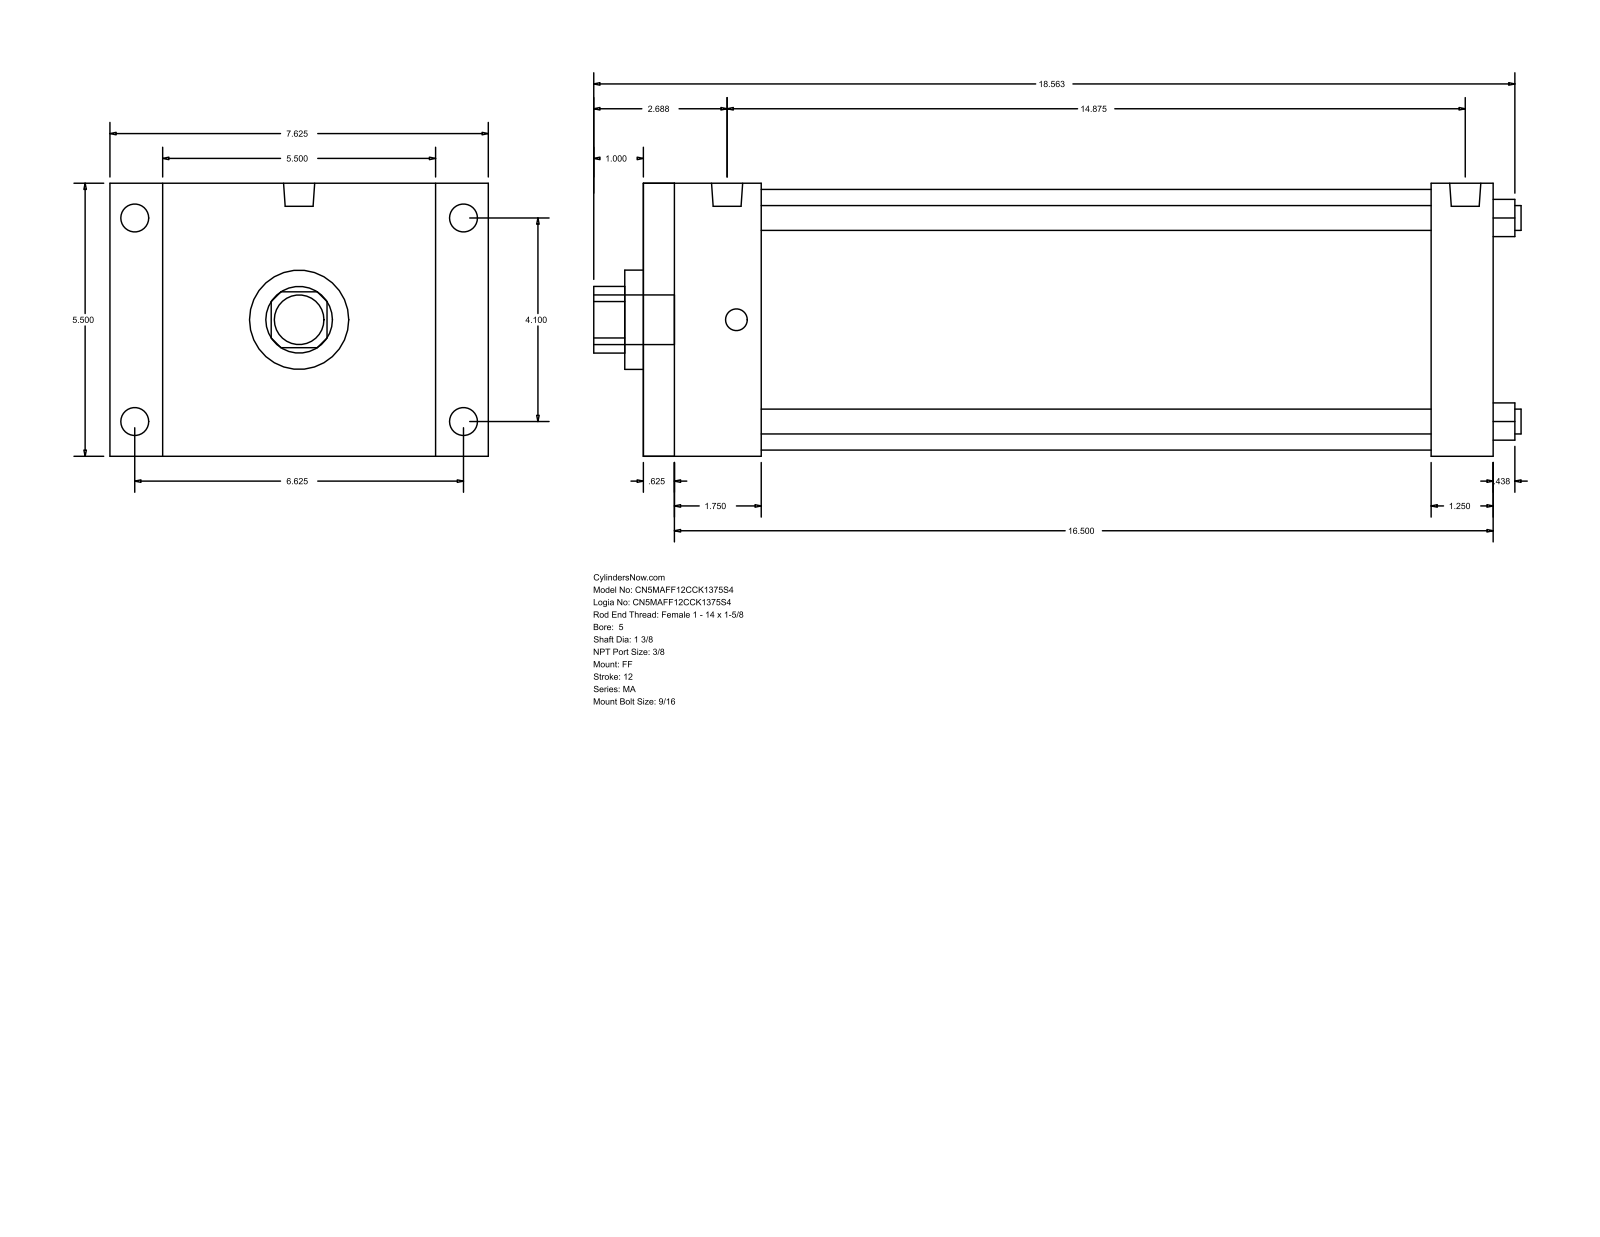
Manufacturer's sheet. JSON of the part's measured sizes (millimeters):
{"part_name": "MA_FF__0500_1.375", "step_written_by": "GSSL Pune (CONFIG_CONTROL_DESIGN)", "units": "millimeters", "bodies": {"solids": 0, "faces": 92, "planar": 64, "cylindrical": 28, "other": 0}, "overall_size": [474.66, 193.68, 139.7], "round_holes": [[12.7, 4], [34.92, 1], [50.8, 1], [133.35, 1]], "round_bosses_or_shafts": [[14.29, 4], [11.11, 4], [15.93, 2], [25.4, 1]], "partial_cylinders_radius": [[17.06, 1]], "face_to_face_distances": [139.7, 434.98, 15.87, 419.11, 403.22, 387.35, 31.76, 60.32, 44.45, 342.9], "hole_center_spacings": [73.64, 104.14, 147.28]}
